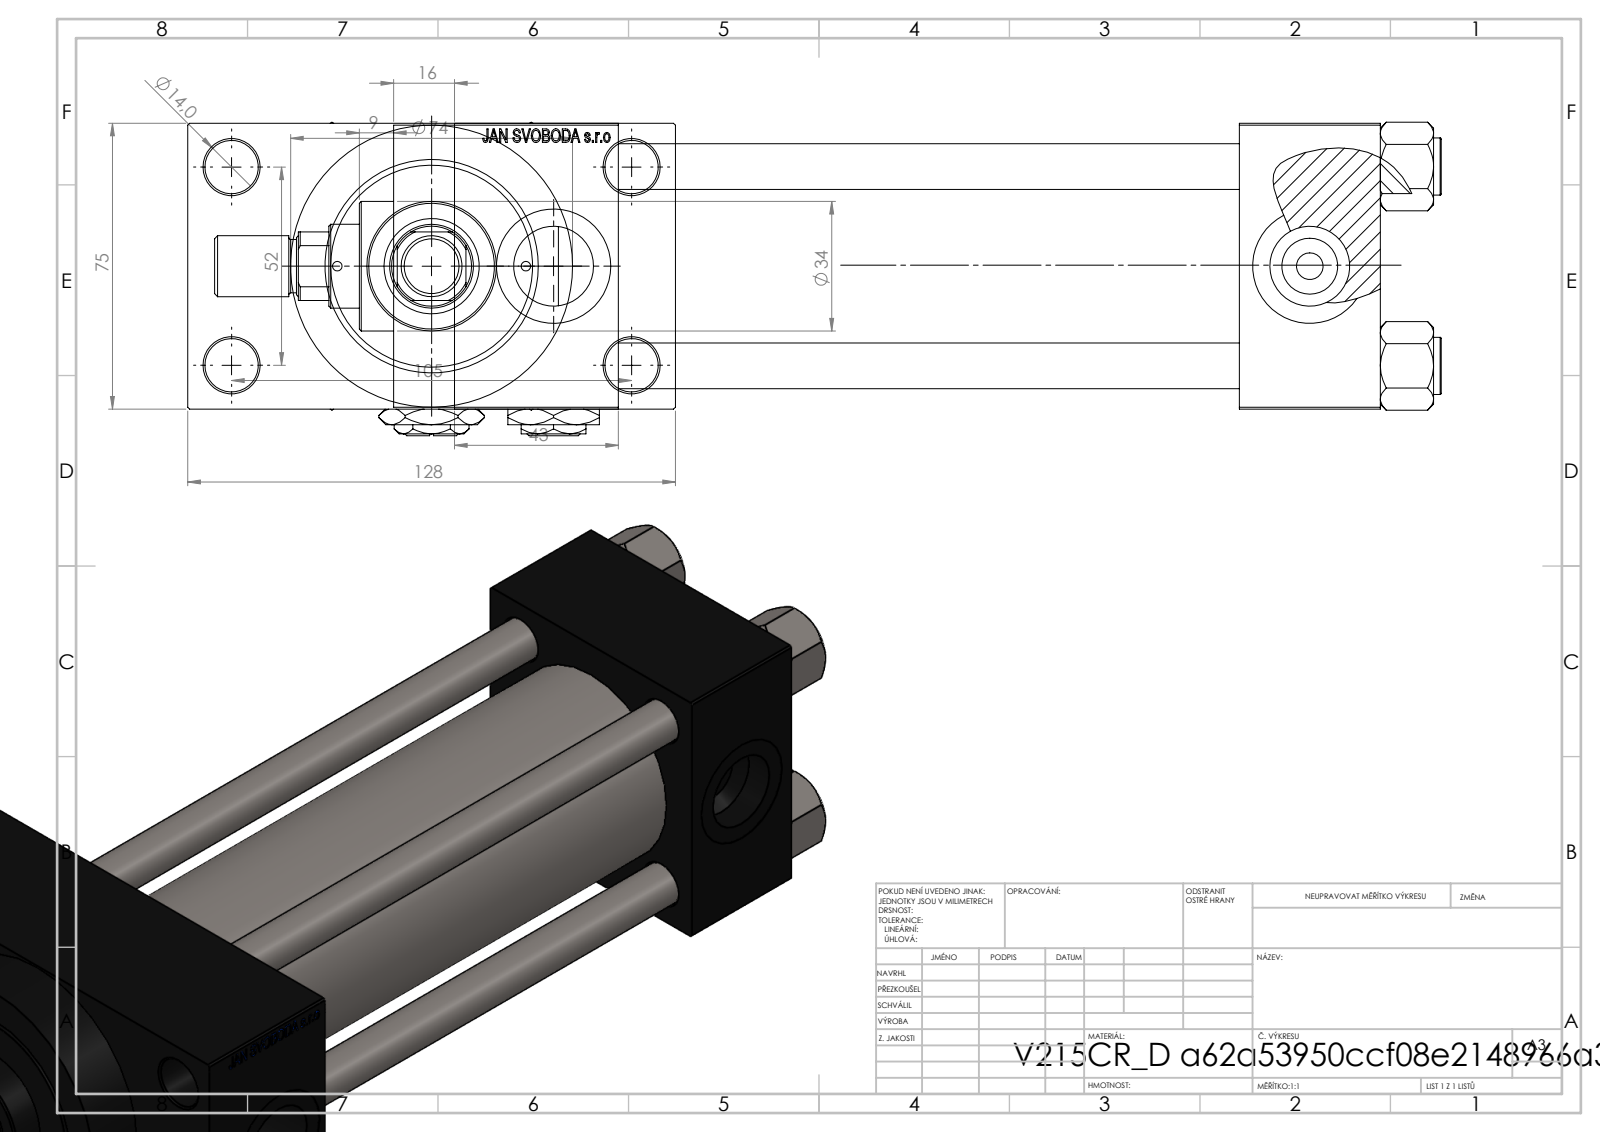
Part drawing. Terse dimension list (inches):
name: V215_VC_A; Zatka_pro_OIL_PORT; V215CR_D_TYCINKA; ROD_END_AH (+3 more)
written by: SolidWorks 2019 (CONFIG_CONTROL_DESIGN)
unit: in
bodies: 13 solids, 1173 faces (527 planar, 100 cylindrical, 546 other)
size: 12.677 × 5.039 × 3.239
volume: 57.34 in³; area: 353 in²
holes: 4× ⌀0.472, 4× ⌀0.551, 3× ⌀0.825, 3× ⌀1.181, 2× ⌀0.098, 2× ⌀0.276, 1× ⌀0.413, 1× ⌀0.866, 1× ⌀0.984, 1× ⌀1.614, 1× ⌀1.969, 1× ⌀2.087
bosses: 4× ⌀0.591, 1× ⌀2.913, 1× ⌀2.205, 1× ⌀1.339, 1× ⌀0.63, 1× ⌀0.551
rounds: 1× R0.413
face distances: 2.953, 6.417, 1.457, 7.874, 1.043, 9.567, 8.11, 1.693, 3.996, 0.63
hole spacings: 1.031, 1.037, 1.456, 1.497, 2.059, 2.253, 2.3, 2.307
